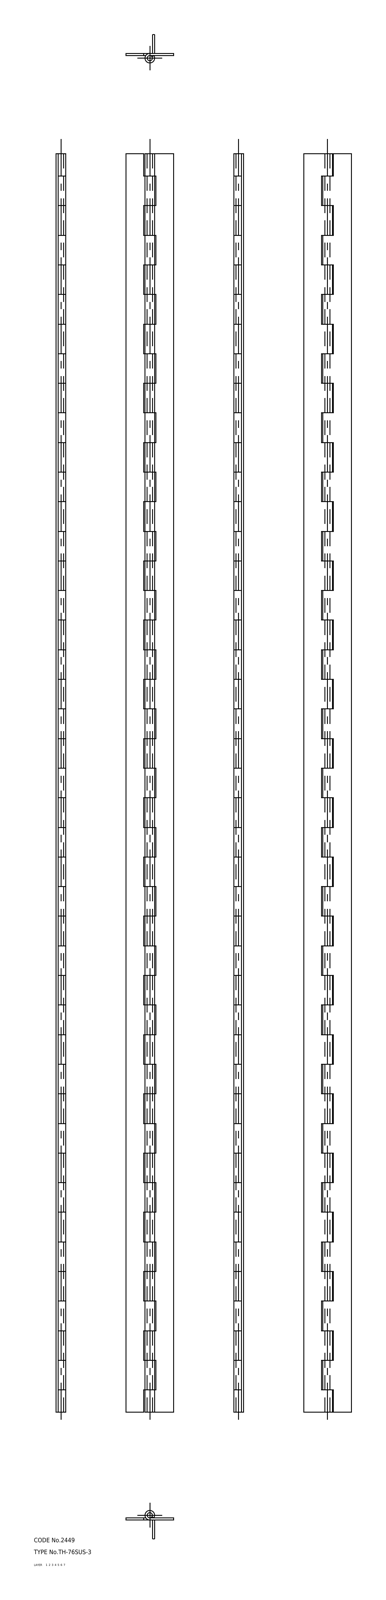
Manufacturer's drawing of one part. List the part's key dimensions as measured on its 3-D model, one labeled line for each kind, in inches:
Part name (STEP PRODUCT): shaft; hinge piece_B; hinge piece_A; TH_76SUS_3_15475_36
STEP written by: CADfix (AUTOMOTIVE_DESIGN)
Units: inches
Bodies: 3 solids, 270 faces (0 planar, 0 cylindrical, 270 other)
Overall size (bounding box): 33.465 × 1.26 × 0.256
Volume: 3.702 in³ · Surface area: 134.4 in²
